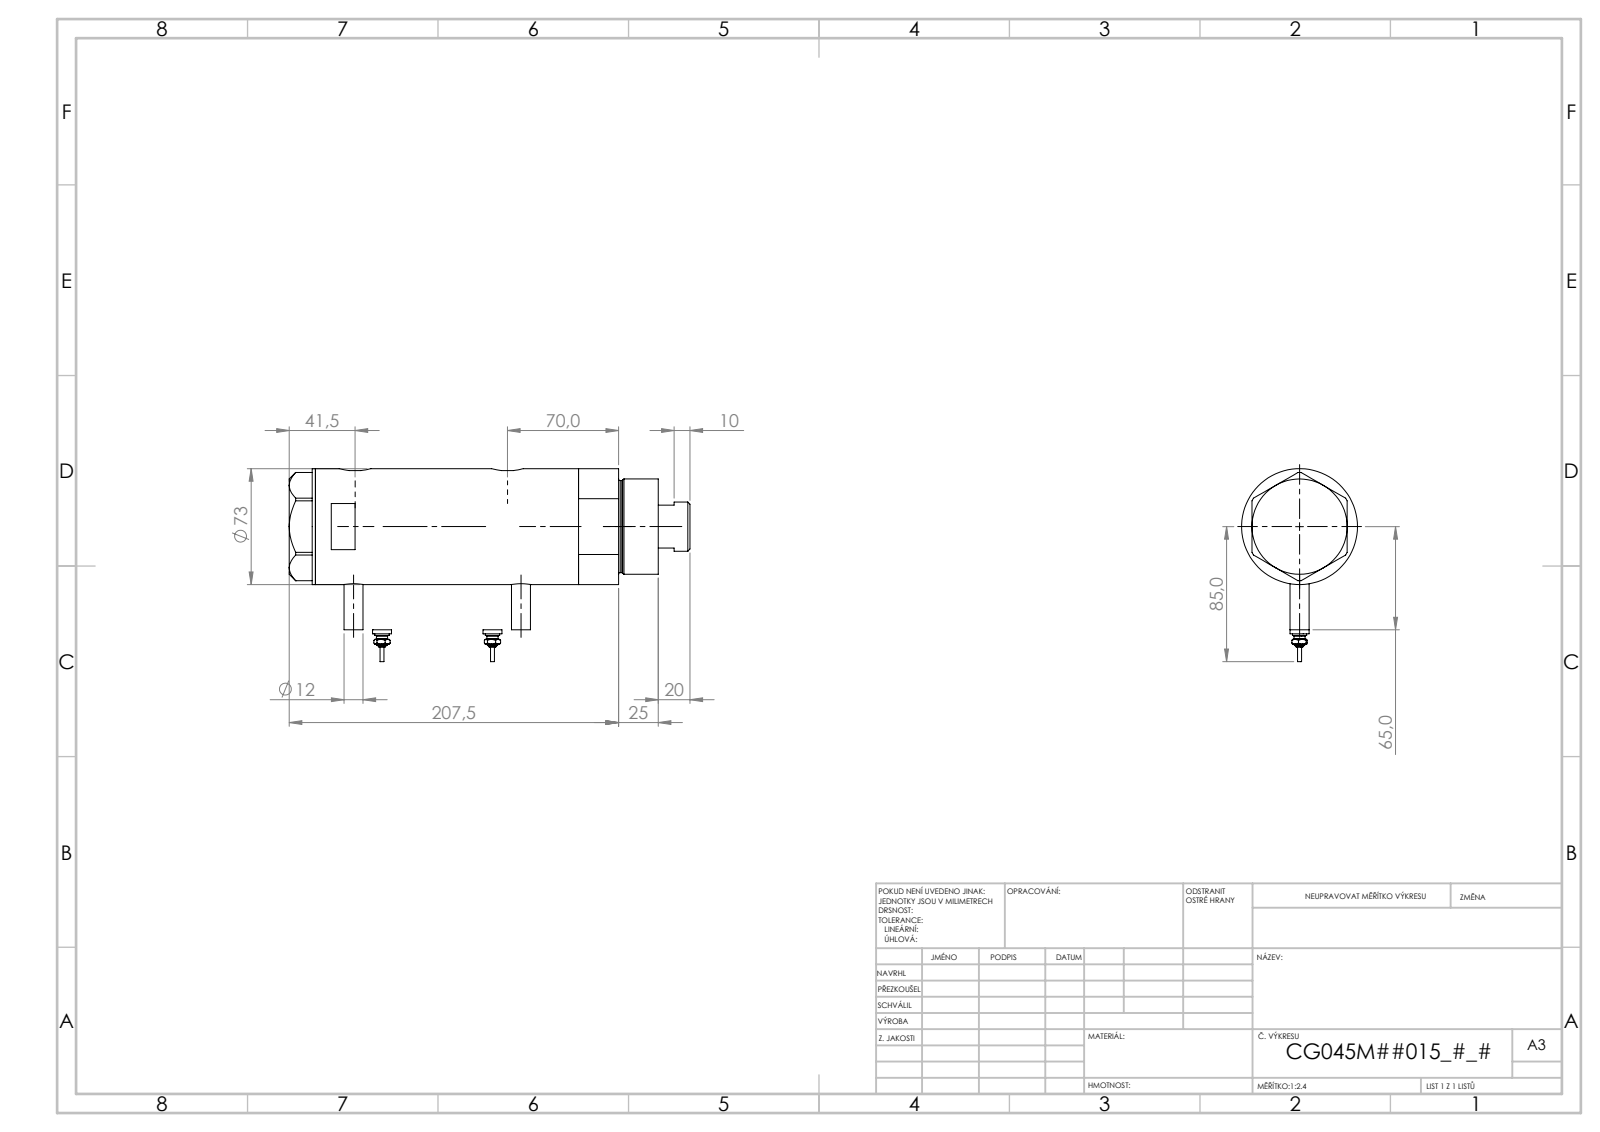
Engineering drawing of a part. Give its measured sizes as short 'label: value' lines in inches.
name: V270CG_MIDDLE; Switch; V270CG_VC; V270CG_BACK (+1 more)
written by: SolidWorks 2019 (CONFIG_CONTROL_DESIGN)
unit: in
bodies: 6 solids, 212 faces (77 planar, 71 cylindrical, 64 other)
size: 9.941 × 4.783 × 2.874
volume: 56.12 in³; area: 237.4 in²
holes: 2× ⌀0.492, 2× ⌀0.518, 1× ⌀0.413, 1× ⌀1.26, 1× ⌀1.319, 1× ⌀1.772, 1× ⌀1.89, 1× ⌀2.52
bosses: 4× ⌀0.472, 2× ⌀0.354, 2× ⌀0.276, 2× ⌀0.177, 2× ⌀0.098, 1× ⌀2.874, 1× ⌀2.362, 1× ⌀2.283
rounds: 2× R0.394
face distances: 3.74, 4.764, 1.024, 0.65, 1.673, 5.413, 0.079, 8.504, 9.154, 7.48
hole spacings: 0.039, 0.335, 3.78, 3.819, 4.114, 4.154
